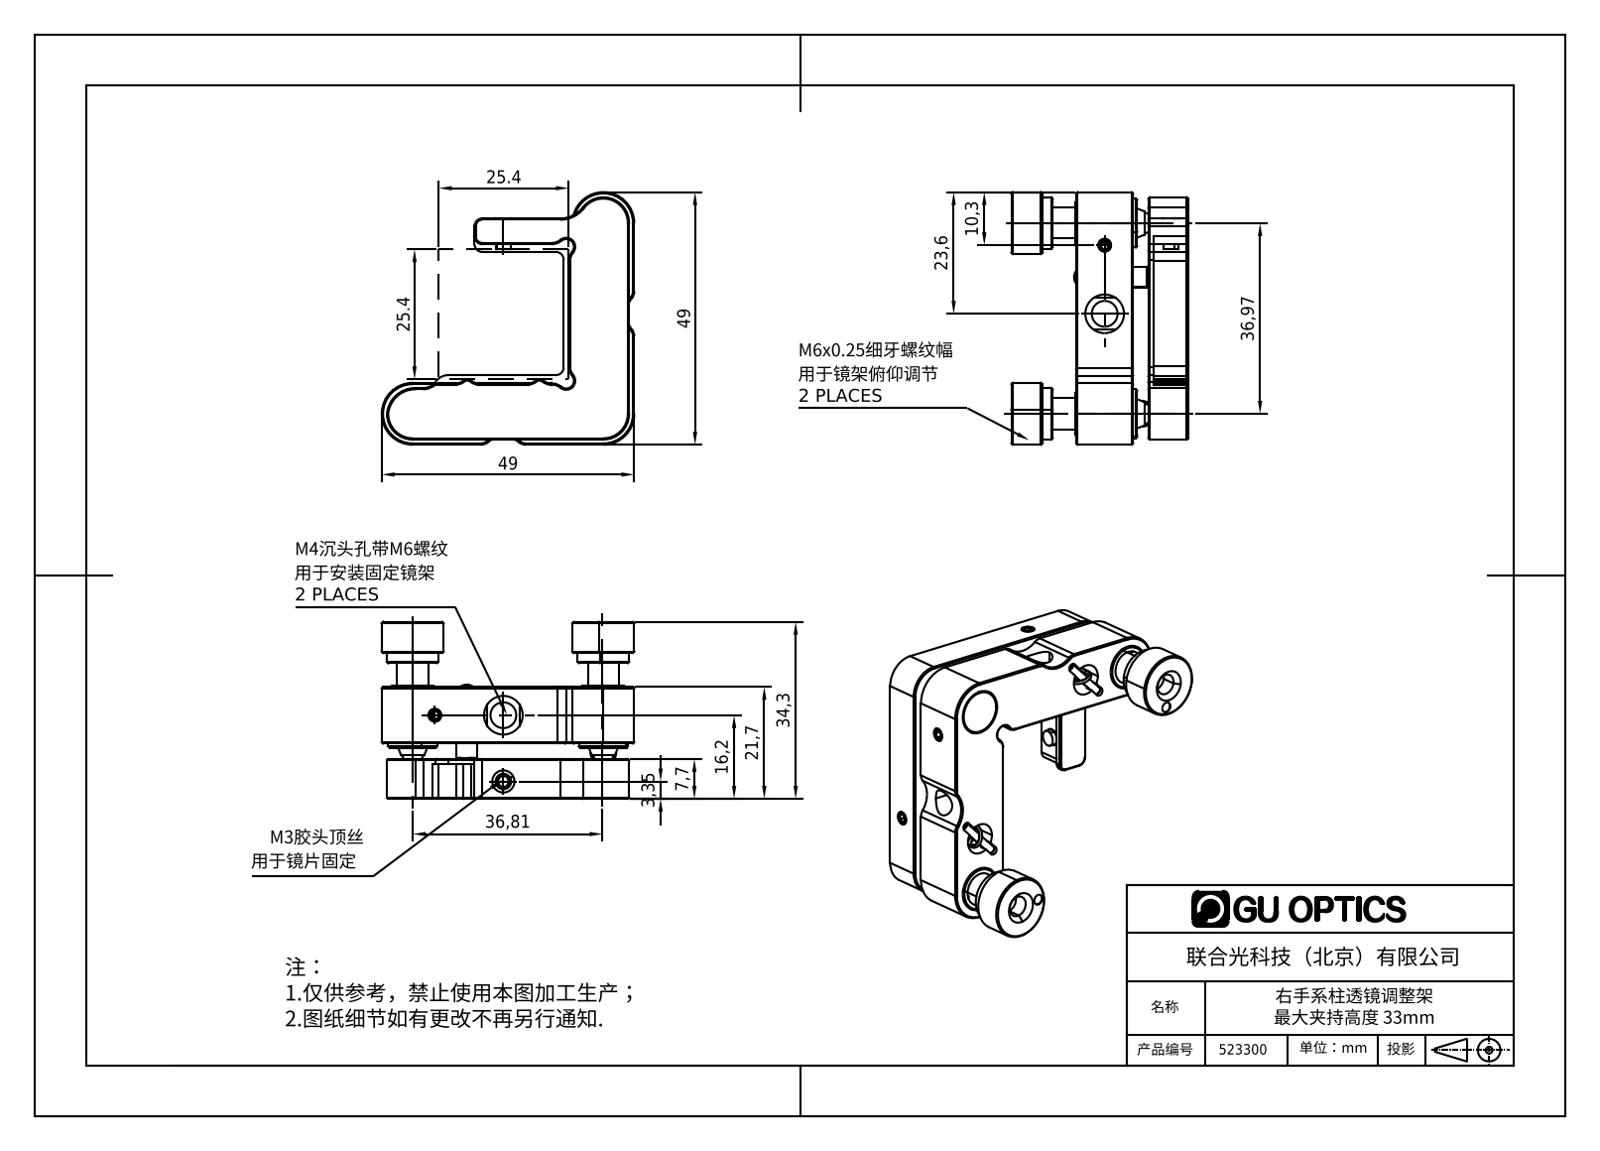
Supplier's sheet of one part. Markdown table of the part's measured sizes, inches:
| quantity | value |
| --- | --- |
| part name | 1.1.7.6_ZJJ-R1-2_标准两轴矩形调整架，高度1.0英寸(25.4mm)，右手系，A |
| STEP written by | SolidWorks 2018 (AUTOMOTIVE_DESIGN) |
| units | inches |
| bodies | 0 solids, 434 faces (133 planar, 124 cylindrical, 177 other) |
| overall size | 1.929 × 1.929 × 1.35 |
| round holes (diameter × count) | 0.098 × 3, 0.339 × 3, 0.079 × 2, 0.157 × 2, 0.197 × 2, 0.236 × 2, 0.295 × 2, 0.13 × 1 |
| round bosses / shafts (diameter × count) | 0.059 × 4, 0.374 × 3, 0.472 × 2, 0.394 × 2, 0.236 × 2, 0.157 × 2, 0.118 × 2 |
| partial cylindrical surfaces (radius × count) | 0.079 × 11, 0.059 × 8, 0.118 × 6, 0.031 × 4, 0.197 × 3, 0.031 × 2, 0.049 × 2, 0.217 × 2 |
| main face-to-face distances | 0.433, 0.303, 0.854, 0.551, 0.039, 0.421, 0.118, 0.472, 0.461, 0.5 |
| hole center spacings | 0.172, 0.413, 0.425, 0.524, 1.043, 1.443, 1.457, 1.677 |
